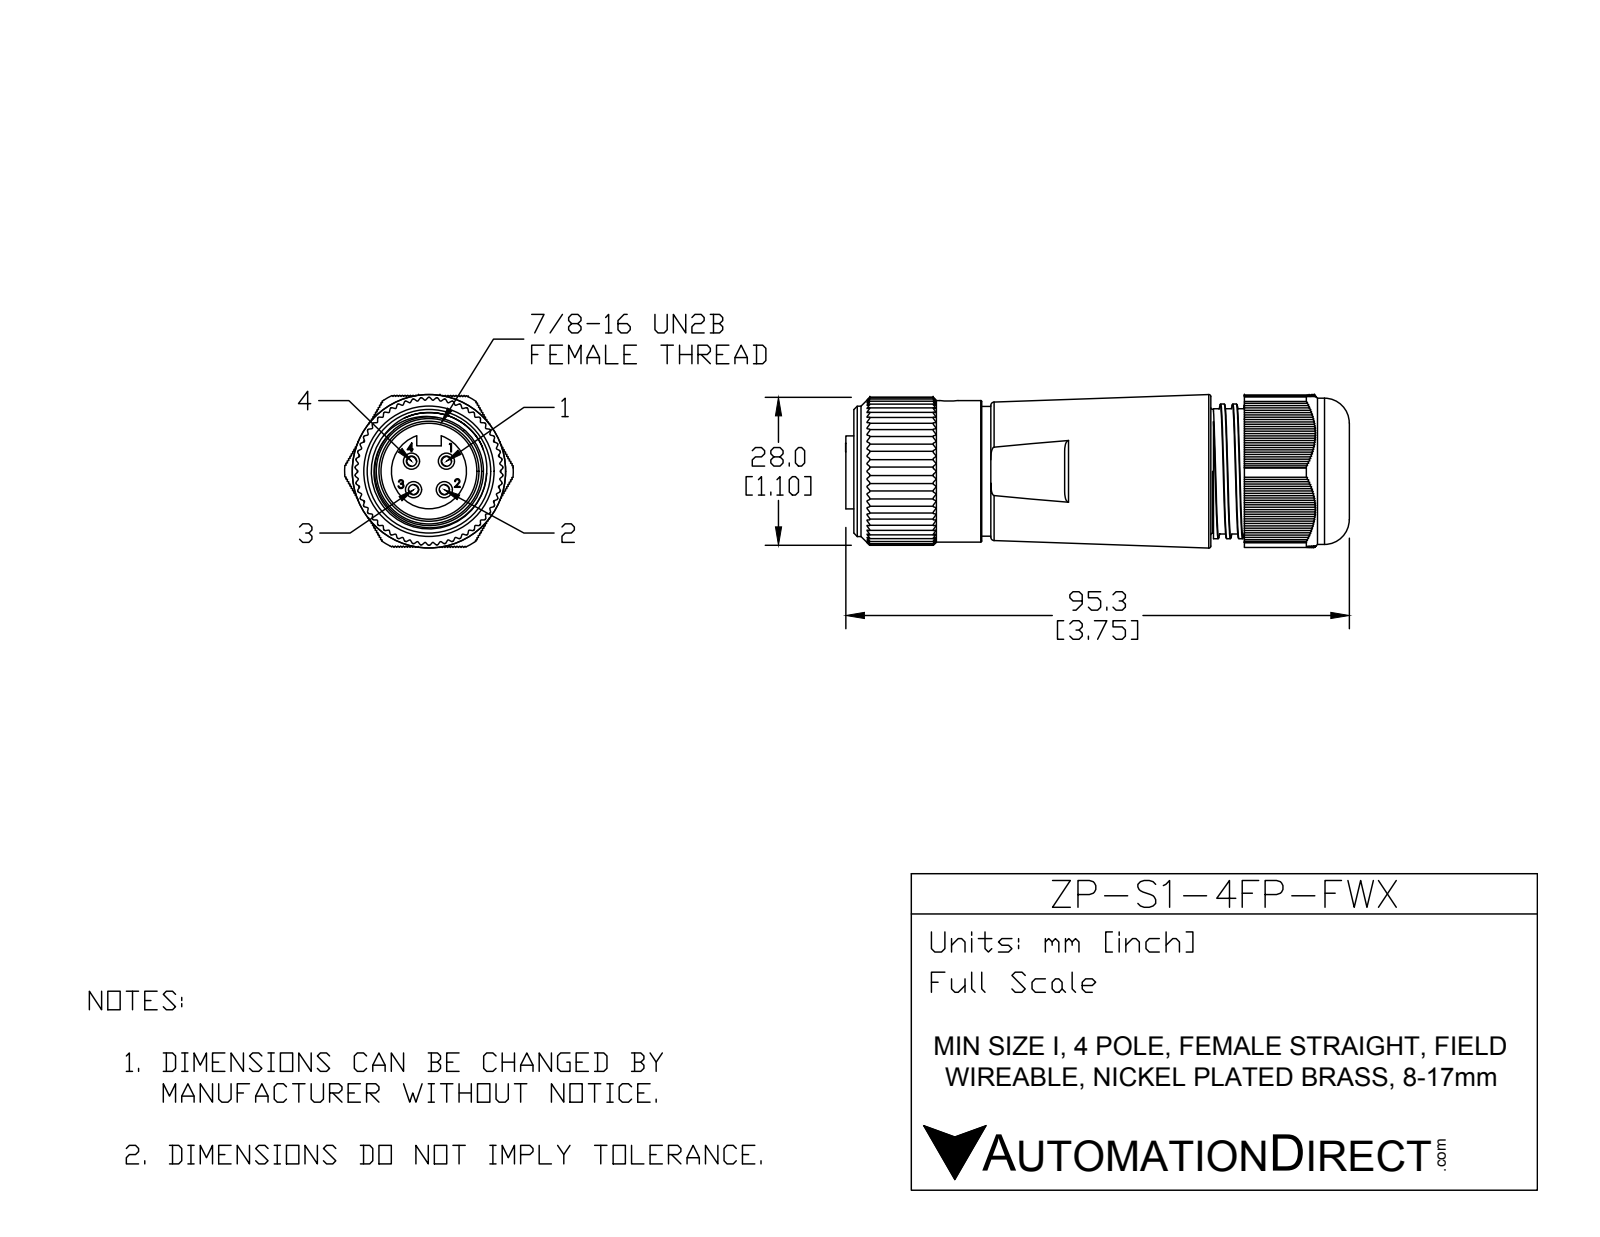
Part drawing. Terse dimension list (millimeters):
name: MIN-4FP-FWX
written by: SolidWorks 2015 (AUTOMOTIVE_DESIGN)
unit: mm
bodies: 1 solid, 1083 faces (685 planar, 337 cylindrical, 61 other)
size: 95.38 × 31.9 × 29.06
volume: 53 578 mm³; area: 15 544 mm²
holes: 4× ⌀3.05, 1× ⌀3.5, 1× ⌀17.27, 1× ⌀20.57, 1× ⌀24.13, 1× ⌀25.4
bosses: 1× ⌀27.69, 1× ⌀26.8, 1× ⌀25.5, 1× ⌀24.68, 1× ⌀24.56, 1× ⌀24, 1× ⌀18.14, 1× ⌀14.22
rounds: 116× R0.25, 58× R0.2, 1× R14, 1× R15.95
face distances: 0.36, 0.72, 6.35, 1.08, 18.94, 69.11, 18.92, 1.44, 18.39, 1.8
hole spacings: 3.81, 4.54, 5.39, 8.22, 5.84, 6.6
